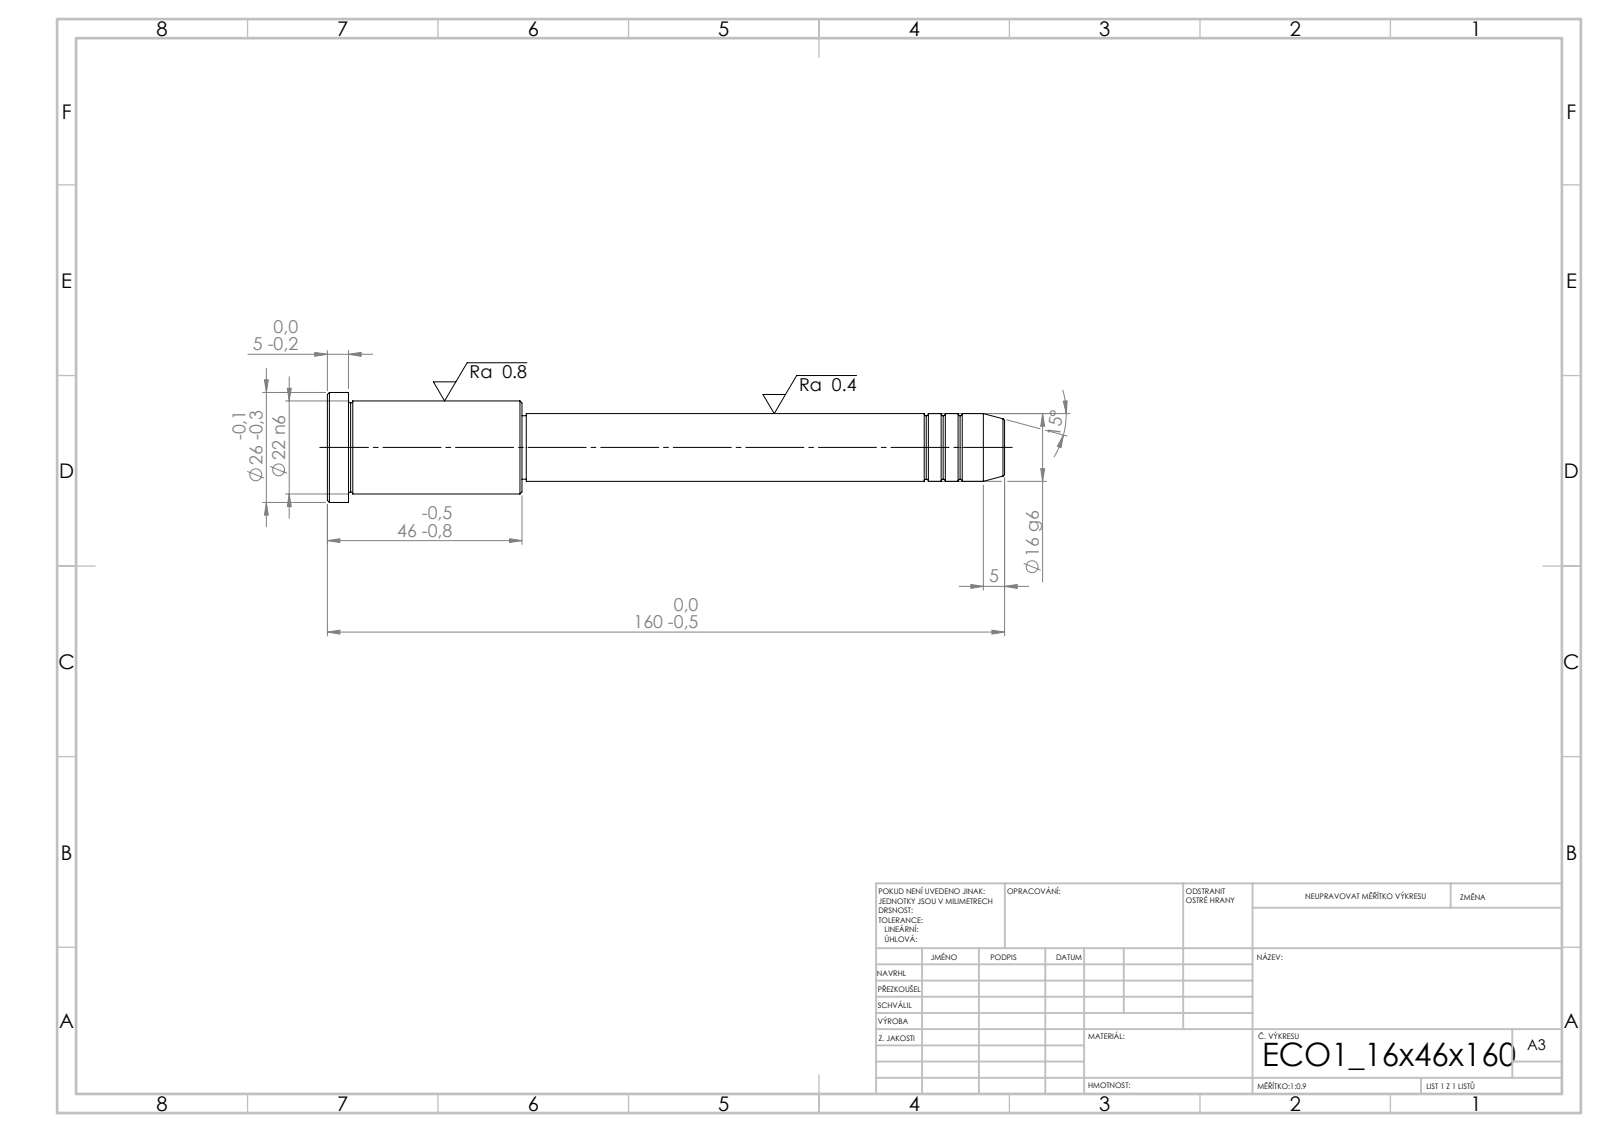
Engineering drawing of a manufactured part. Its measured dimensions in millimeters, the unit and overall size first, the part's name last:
Units: millimetres
Overall size (bounding box): 160 × 26 × 26
Round bosses / shafts (diameter × count): ⌀26 ×1, ⌀22 ×1, ⌀16 ×1, ⌀15 ×1
Main face-to-face distances: 46, 41, 5, 114, 155, 160, 113, 1, 42, 47
Volume: 40 874 mm³ · Surface area: 10 069 mm²
Bodies: 1 solid, 43 faces (5 planar, 14 cylindrical, 24 other)
STEP written by: SolidWorks 2019 (CONFIG_CONTROL_DESIGN)
